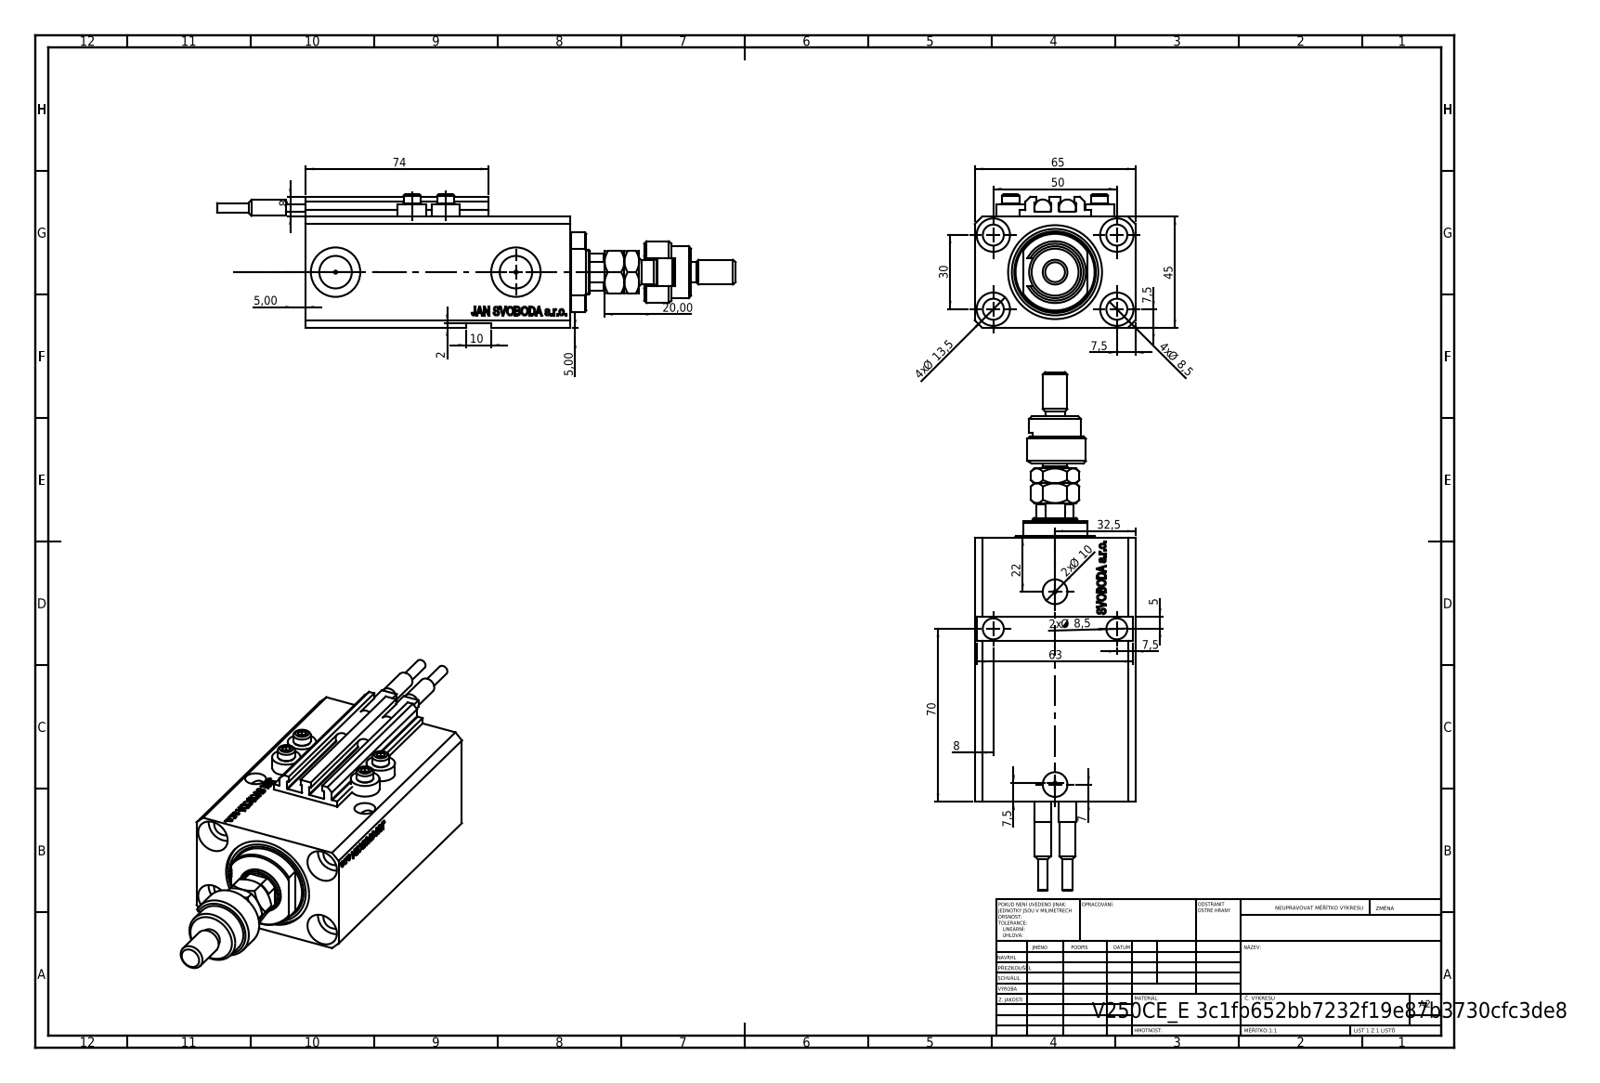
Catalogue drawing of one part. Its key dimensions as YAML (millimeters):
part_name: "V250CE_C_VCP; FEMALE_PART_FOR_DFA; SWITCH_V250CE; V250CE_VC_E (+3 more)"
step_written_by: "SolidWorks 2019 (CONFIG_CONTROL_DESIGN)"
units: millimeters
bodies: {solids: 12, faces: 1204, planar: 571, cylindrical: 151, other: 482}
overall_size: [209.9, 65, 54]
volume: 292227
surface_area: 86156
round_holes:
  - {diameter: 8.5, count: 7}
  - {diameter: 1.25, count: 4}
  - {diameter: 4, count: 4}
  - {diameter: 13.5, count: 4}
  - {diameter: 10, count: 2}
  - {diameter: 13.16, count: 2}
  - {diameter: 20, count: 2}
  - {diameter: 18, count: 1}
  - {diameter: 38, count: 1}
round_bosses_or_shafts:
  - {diameter: 11.6, count: 4}
  - {diameter: 7, count: 4}
  - {diameter: 6.8, count: 2}
  - {diameter: 6.5, count: 2}
  - {diameter: 4, count: 2}
  - {diameter: 25, count: 1}
  - {diameter: 21, count: 1}
  - {diameter: 16, count: 1}
partial_cylinders:
  - {radius: 0.2, count: 10}
  - {radius: 5.5, count: 1}
  - {radius: 8.5, count: 1}
  - {radius: 8.75, count: 1}
  - {radius: 16, count: 1}
face_to_face_distances: [45, 65, 2, 81.9, 47, 3, 25.1, 107, 75, 10]
hole_center_spacings: [29.15, 50, 13.6, 15.12, 27.89, 30, 33.62, 36]
